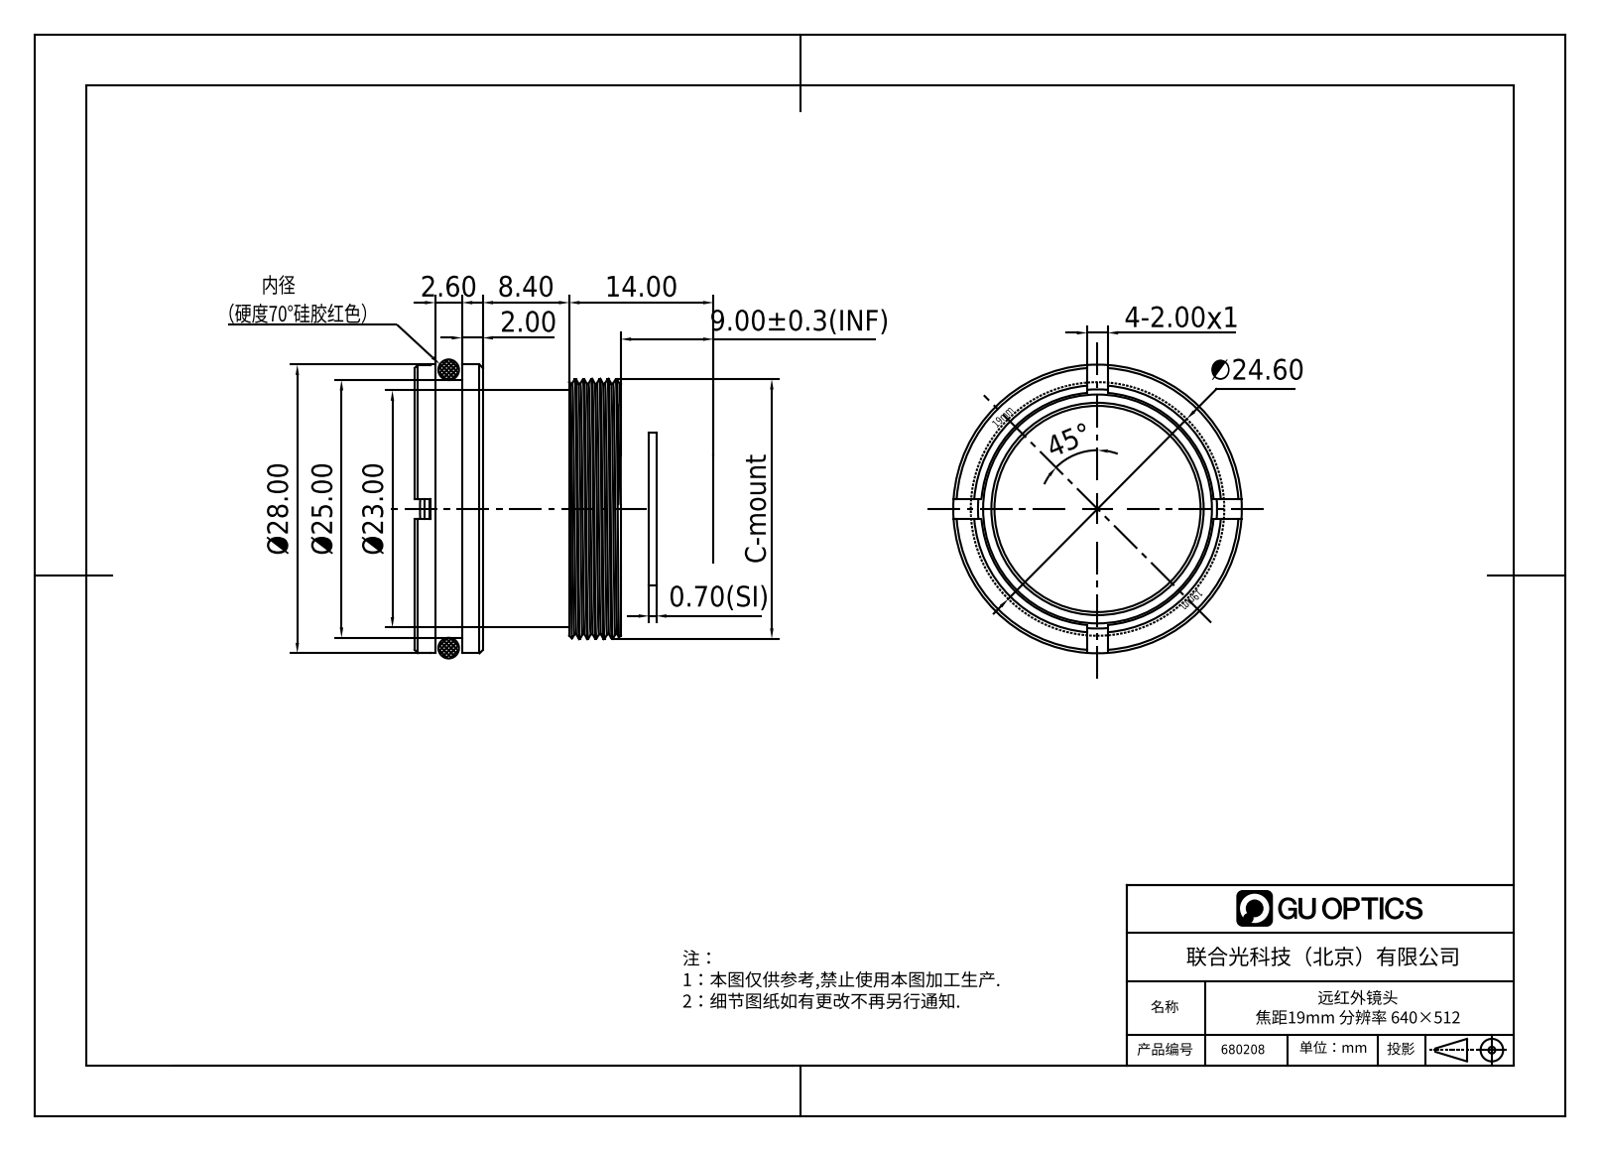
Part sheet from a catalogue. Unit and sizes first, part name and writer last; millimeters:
Units: millimetres
Overall size (bounding box): 28 × 28 × 20
Round holes (diameter × count): ⌀20 ×1, ⌀23 ×1, ⌀24.32 ×1, ⌀25 ×1, ⌀25.18 ×1, ⌀28 ×1
Round bosses / shafts (diameter × count): ⌀23.4 ×1, ⌀23.2 ×1, ⌀22.6 ×1, ⌀21.4 ×1, ⌀18.6 ×1, ⌀17.4 ×1
Main face-to-face distances: 2, 4.6, 13.4, 15.4, 2.6, 18, 6.6, 20, 0.8, 7.4
Bodies: 0 solids, 69 faces (30 planar, 14 cylindrical, 25 other)
Part name (STEP PRODUCT): 680208
STEP written by: SolidWorks 2020 (CONFIG_CONTROL_DESIGN)
